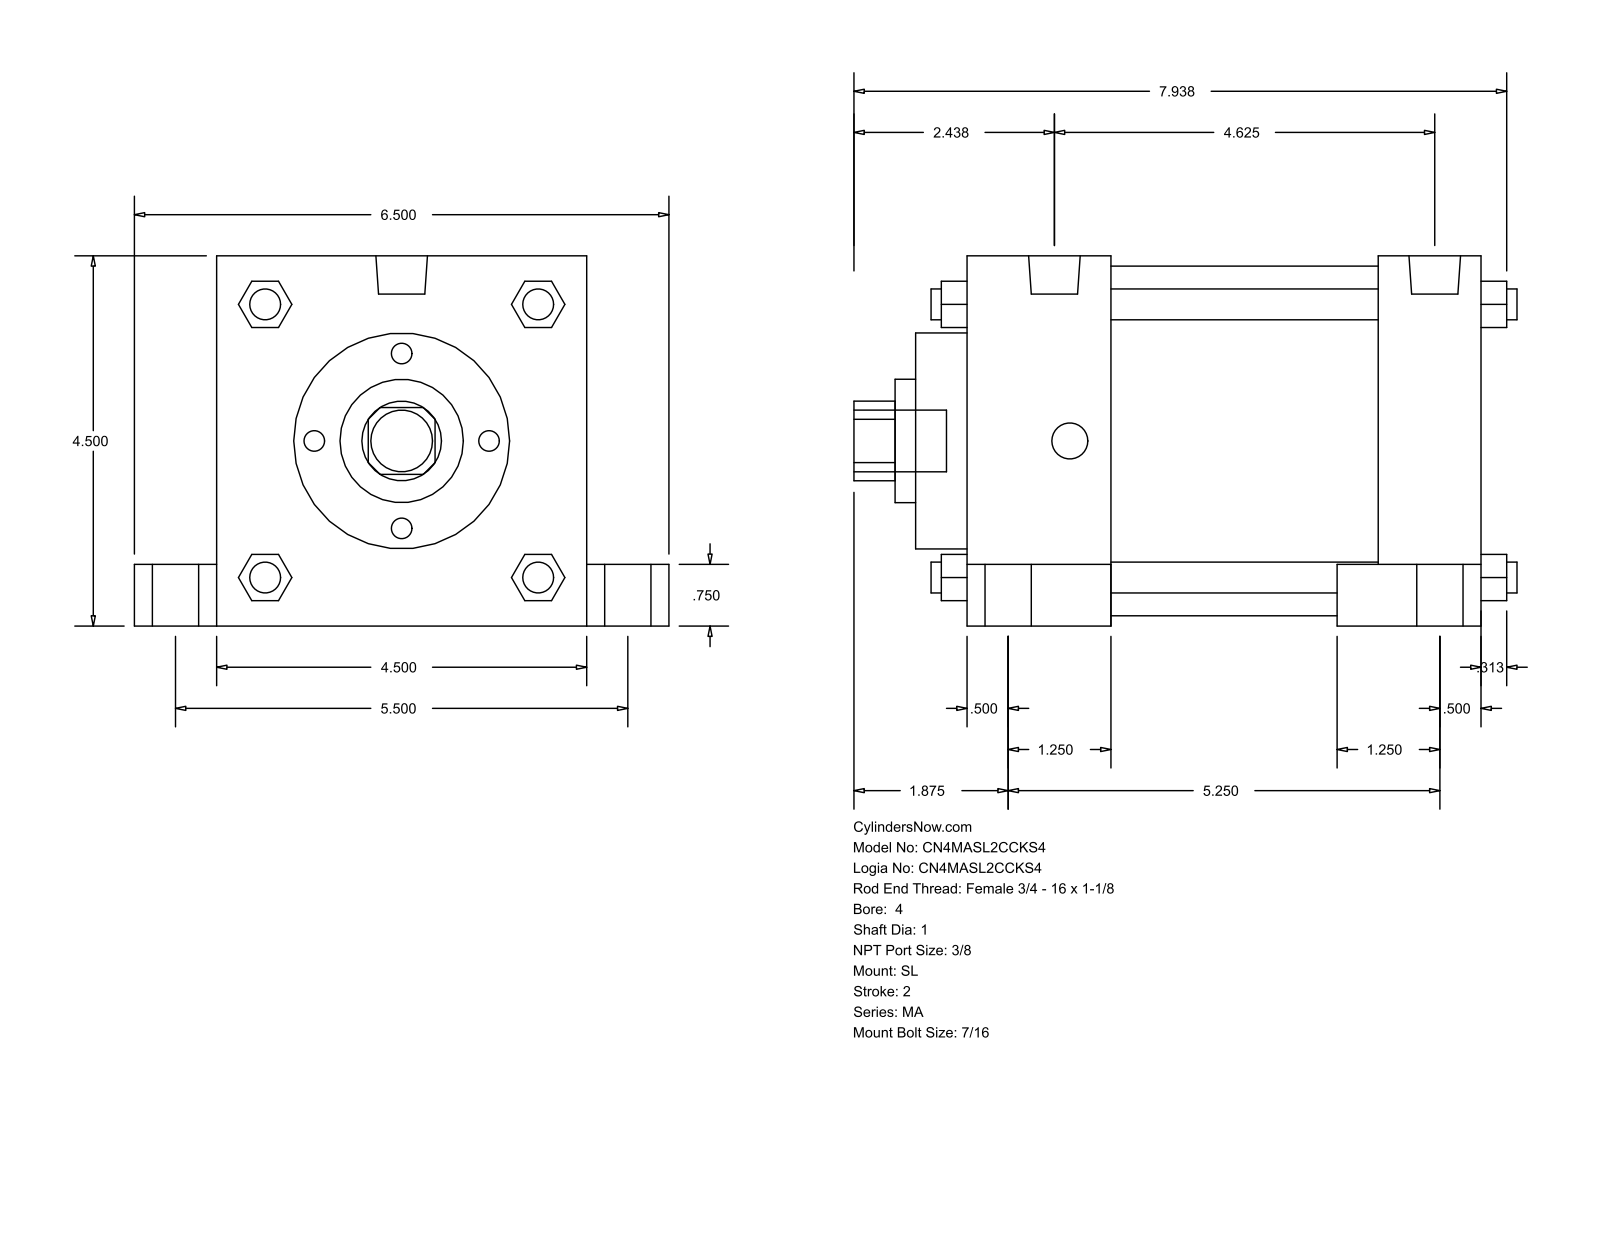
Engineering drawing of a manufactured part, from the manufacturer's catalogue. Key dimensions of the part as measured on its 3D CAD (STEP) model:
Part name (STEP PRODUCT): MA_SL__0400_1
STEP written by: GSSL Pune (CONFIG_CONTROL_DESIGN)
Units: millimetres
Bodies: 0 solids, 150 faces (113 planar, 37 cylindrical, 0 other)
Overall size (bounding box): 204.79 × 165.1 × 114.3
Round holes (diameter × count): ⌀25.4 ×1, ⌀38.1 ×1, ⌀66.67 ×1, ⌀107.95 ×1
Round bosses / shafts (diameter × count): ⌀20.64 ×4, ⌀14.29 ×4, ⌀11.11 ×4, ⌀9.53 ×4, ⌀15.93 ×2, ⌀19.05 ×1
Partial cylindrical surfaces — rounded edges, fillets, slot ends (radius × count): R12.29 ×1
Main face-to-face distances: 114.3, 158.76, 82.55, 44.46, 127.01, 31.75, 25.4, 139.7, 19.05, 15.87
